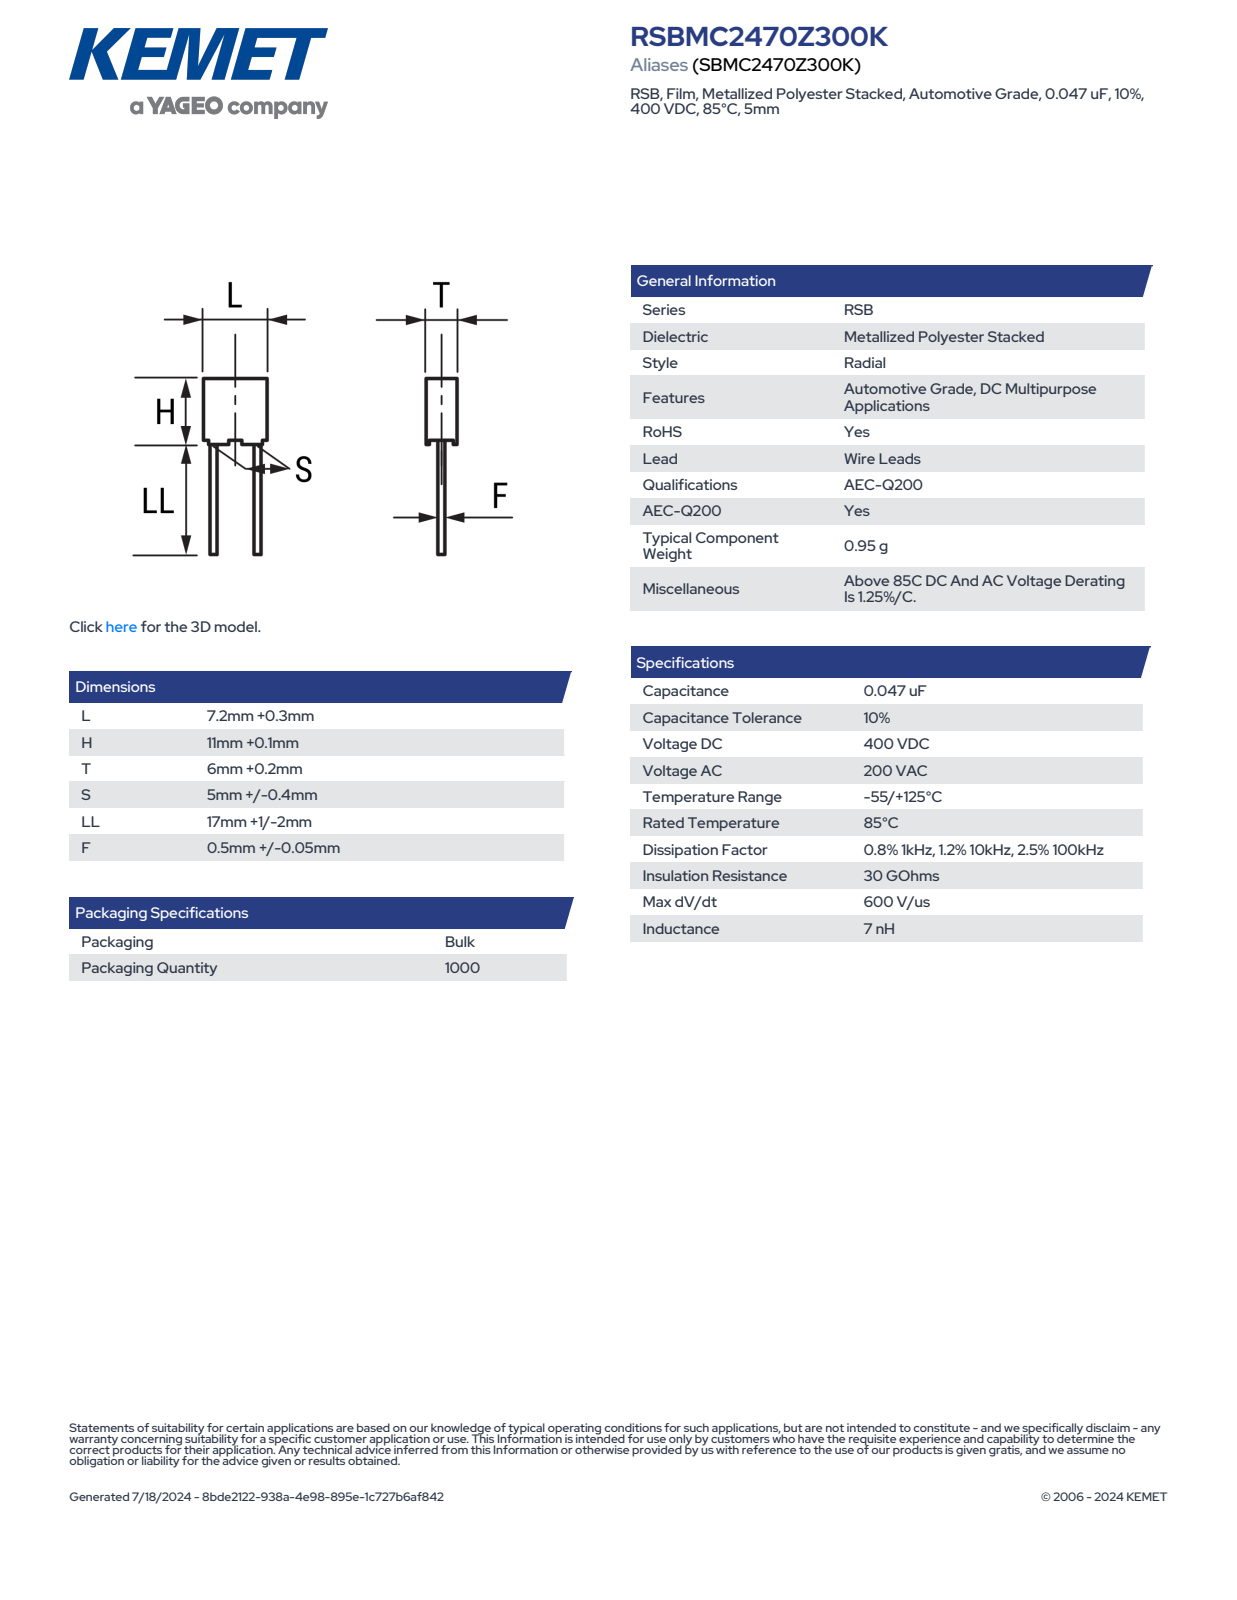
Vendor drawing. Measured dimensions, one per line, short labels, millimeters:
name: CFR_RB3_7.2X11X6_L7.5H11.1T6.2S5LL18F0.65
written by: SolidWorks 2014 (AUTOMOTIVE_DESIGN)
unit: mm
bodies: 4 solids, 85 faces (77 planar, 8 cylindrical, 0 other)
size: 29.1 × 7.5 × 6.21
volume: 497 mm³; area: 489 mm²
bosses: 2× ⌀0.65
rounds: 4× R0.5
face distances: 6.2, 7.5, 10.35, 5.95, 7.25, 0.75, 11.1, 5.7, 7, 0.38
